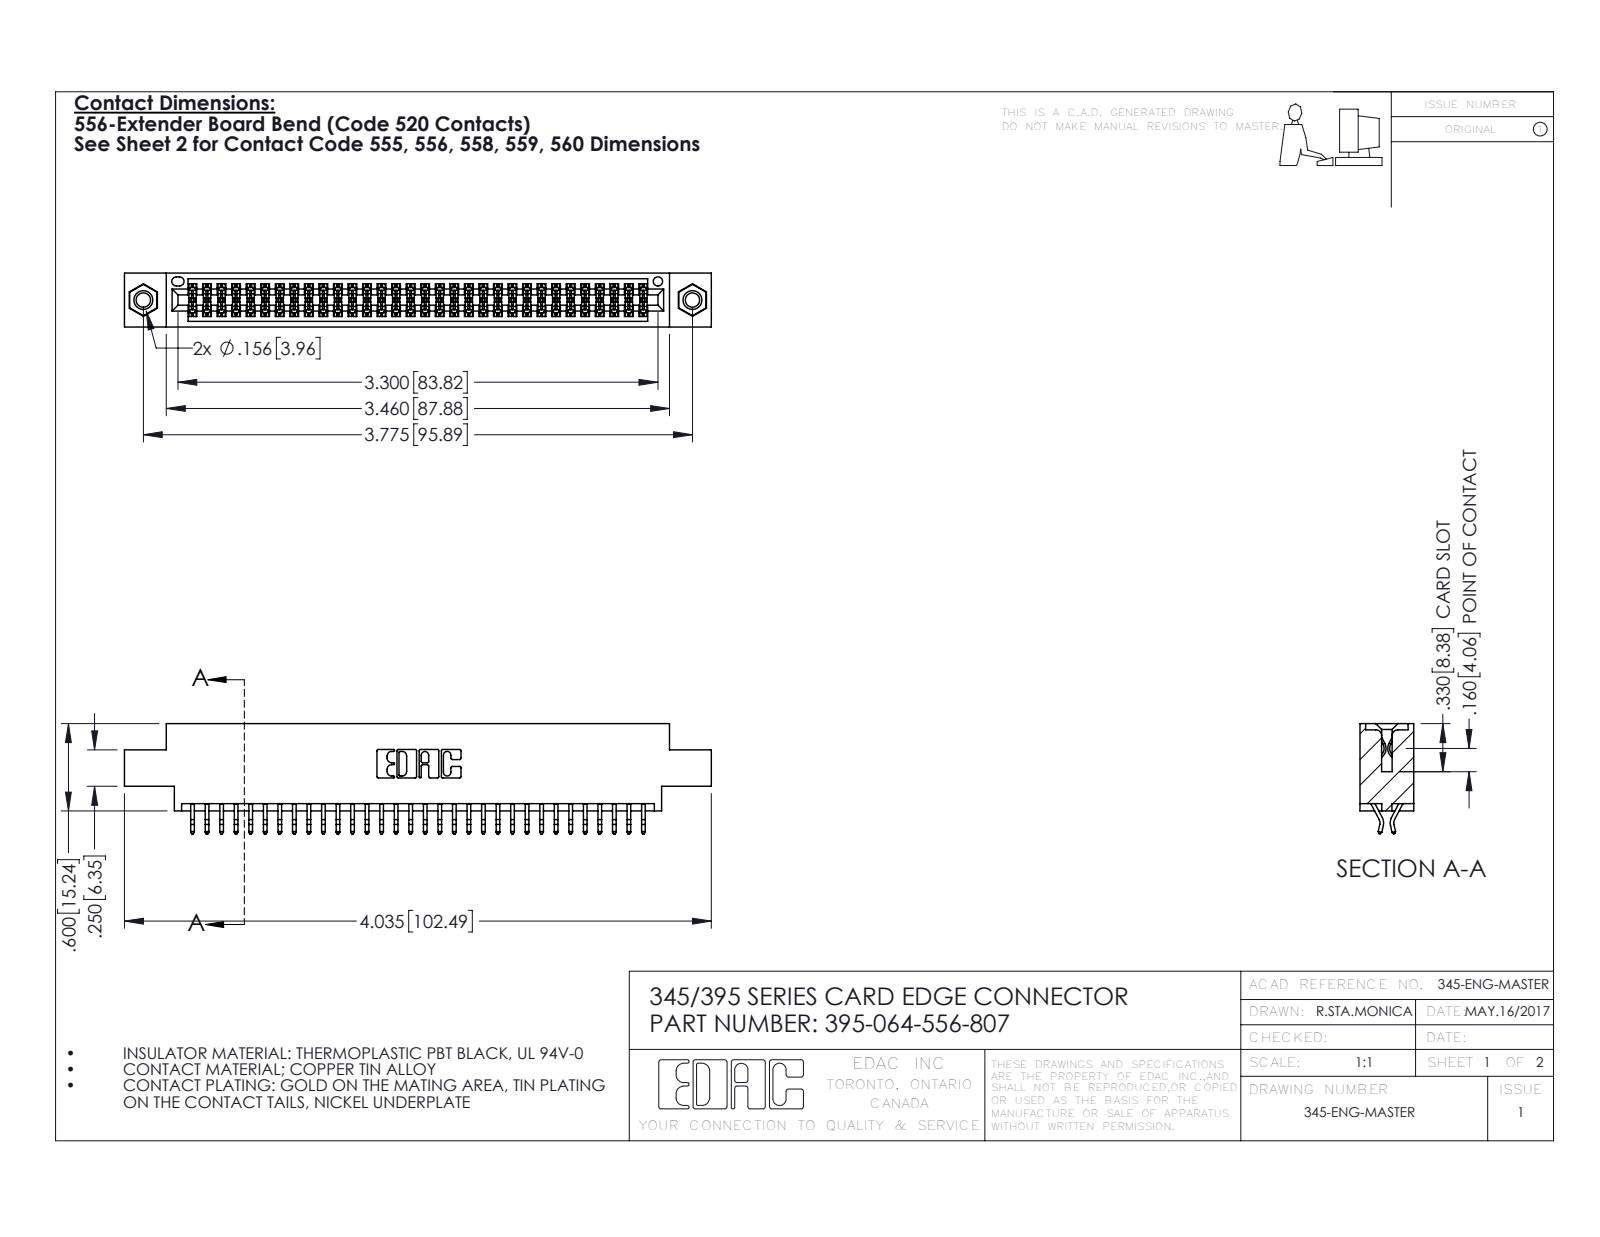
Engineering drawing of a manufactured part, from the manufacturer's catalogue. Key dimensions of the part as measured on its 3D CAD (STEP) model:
Part name (STEP PRODUCT): 345-250-001_345-250-005-103; 345 Part_0.170 Offset - 0.156 Dia-TI; 395-064-556-807; 345-292-001_556 Tail
STEP written by: SolidWorks 2016 (CONFIG_CONTROL_DESIGN)
Units: inches
Bodies: 67 solids, 3774 faces (2484 planar, 1274 cylindrical, 16 other)
Overall size (bounding box): 4.035 × 0.757 × 0.37
Volume: 0.594 in³ · Surface area: 22.18 in²
Round holes (diameter × count): ⌀0.098 ×2, ⌀0.125 ×2, ⌀0.156 ×2, ⌀0.064 ×1
Round bosses / shafts (diameter × count): ⌀0.155 ×2
Partial cylindrical surfaces — rounded edges, fillets, slot ends (radius × count): R0.006 ×96, R0.01 ×22, R0.007 ×6, R0.031 ×6, R0.026 ×3, R0.01 ×2, R0.014 ×2, R0.019 ×2
Main face-to-face distances: 0.072, 0.298, 0.37, 0.2, 0.025, 0.098, 0.272, 0.225, 0.175, 0.149
Hole centre spacings: 0.27, 3.54, 3.775
